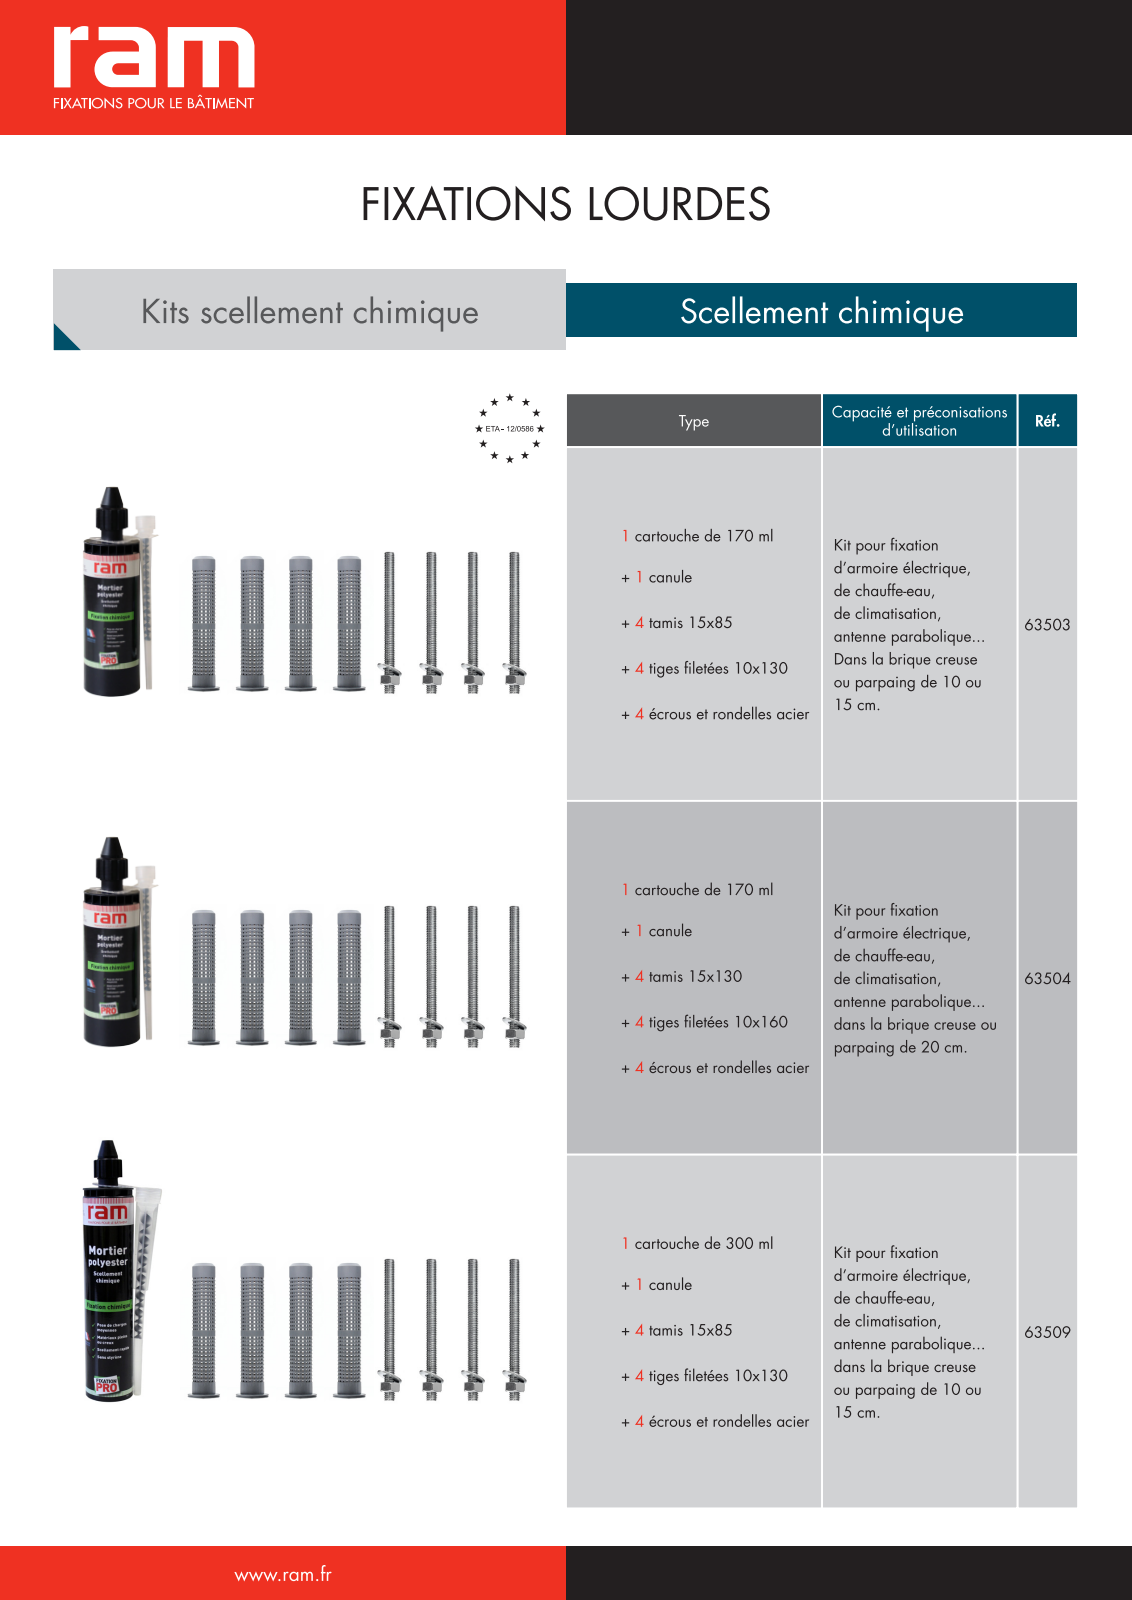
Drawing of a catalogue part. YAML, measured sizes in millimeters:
step_written_by: "ACIS (automotive_design)"
units: millimeters
bodies: {solids: 2, faces: 24, planar: 8, cylindrical: 10, other: 6}
overall_size: [75, 3, 3]
volume: 523
surface_area: 723
round_bosses_or_shafts:
  - {diameter: 3, count: 1}
partial_cylinders:
  - {radius: 0.24, count: 1}
  - {radius: 0.39, count: 1}
  - {radius: 0.54, count: 1}
  - {radius: 1.4, count: 1}
face_to_face_distances: [73.5, 26.39, 47.11]
